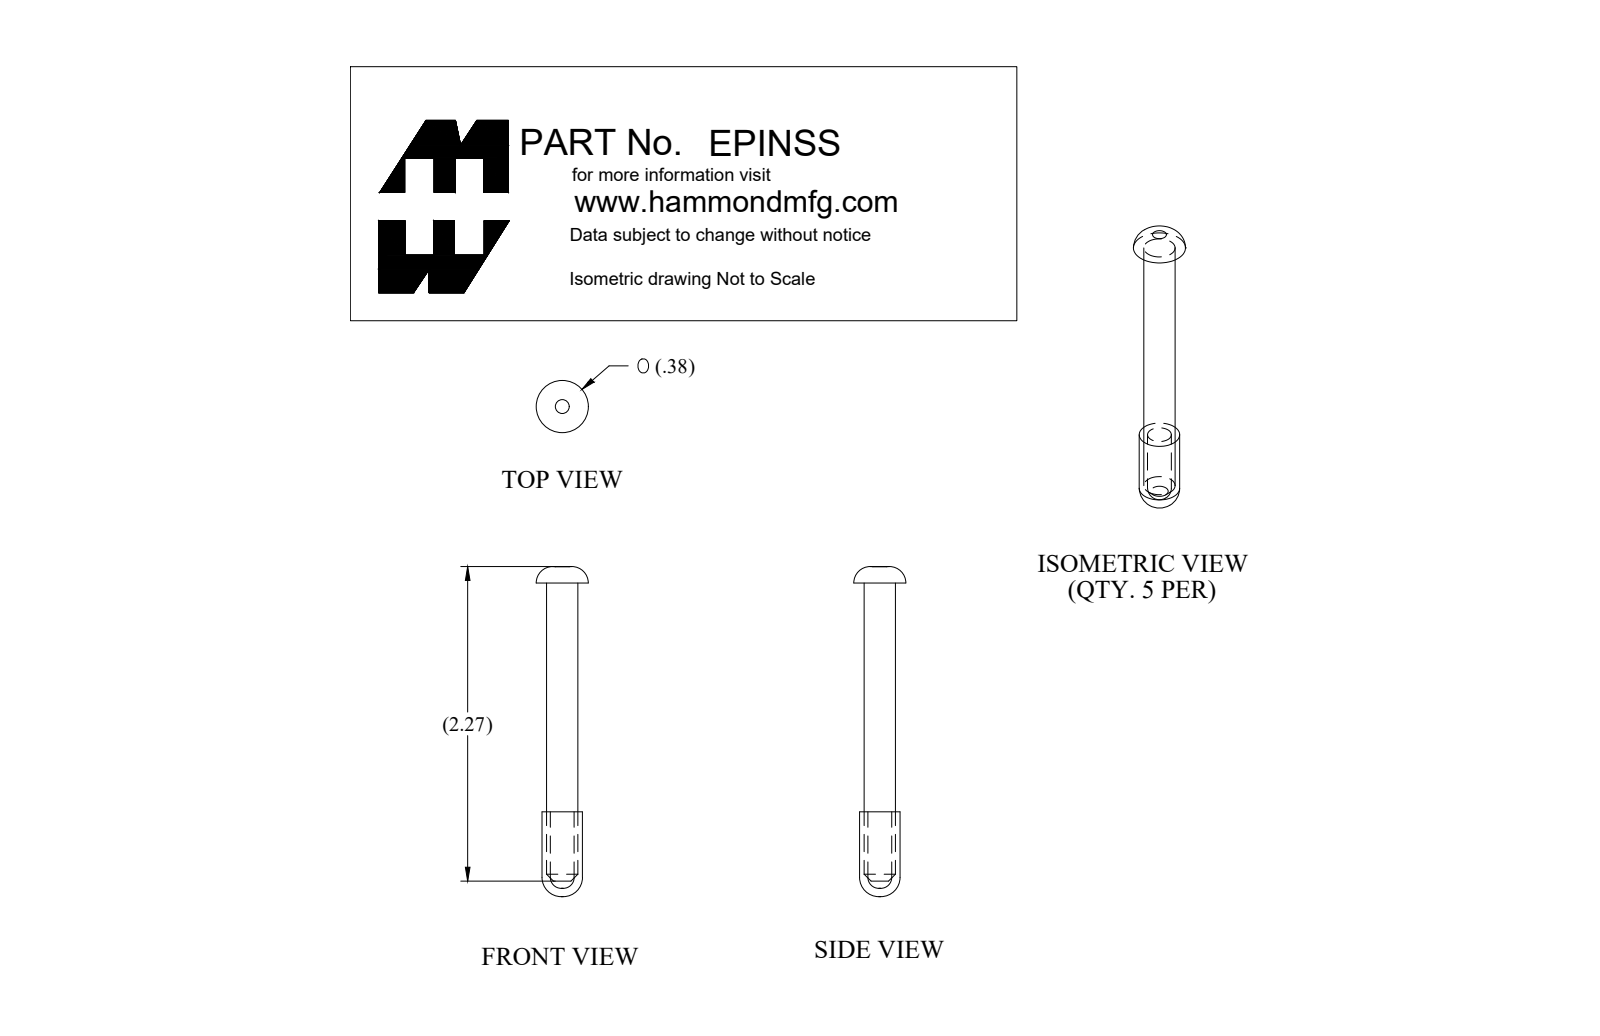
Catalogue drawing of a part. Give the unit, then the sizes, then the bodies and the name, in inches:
Units: inches
Overall size (bounding box): 2.381 × 0.376 × 0.376
Round holes (diameter × count): ⌀0.172 ×1
Round bosses / shafts (diameter × count): ⌀0.292 ×1, ⌀0.226 ×1
Main face-to-face distances: 1.65, 0.5, 2.15, 2.267, 1.767, 0.117
Volume: 0.121 in³ · Surface area: 2.708 in²
Bodies: 2 solids, 18 faces (4 planar, 6 cylindrical, 8 other)
Part name (STEP PRODUCT): EPINSS
STEP written by: SolidWorks 2018 (AUTOMOTIVE_DESIGN)
